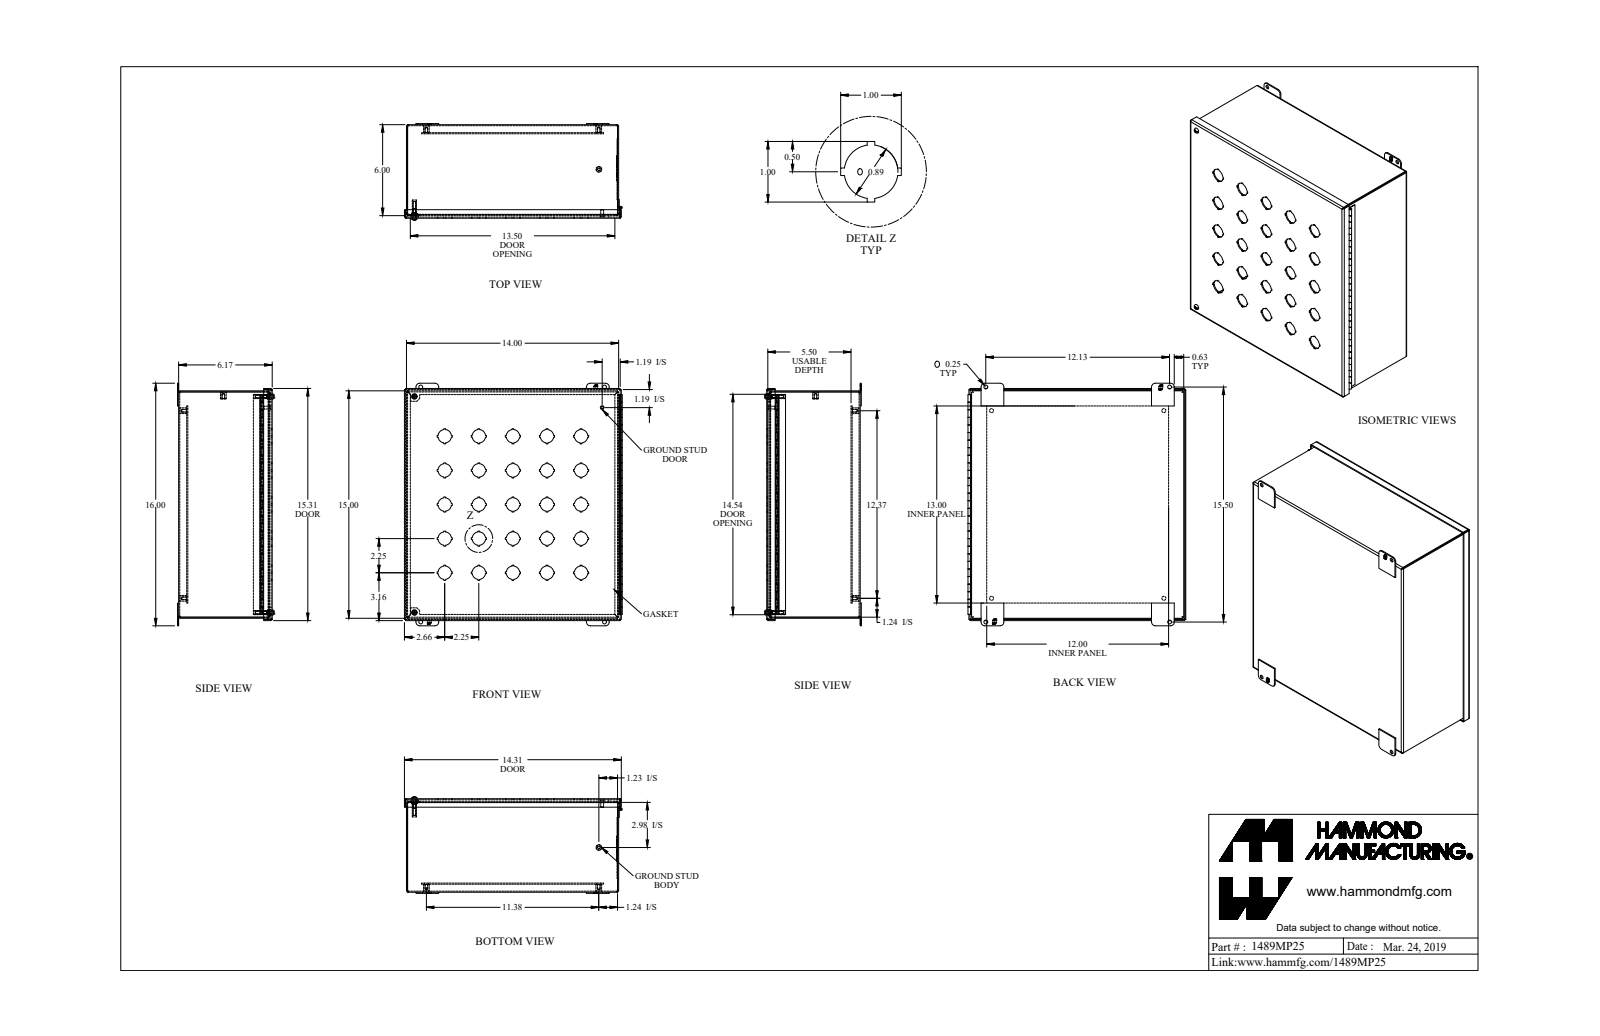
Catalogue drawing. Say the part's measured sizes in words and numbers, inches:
The part is named "1489MP25_Default". Its 3-D file was written by "SolidWorks 2019 (CONFIG_CONTROL_DESIGN)". It is 21 solids with 1167 faces: 814 planar, 295 cylindrical and 58 other. Overall it measures 16 by 14.373 by 6.371 inches. Its volume is 77.55 cubic inches and its surface area 2 084 square inches. Round holes: 25 of diameter 0.886, 6 of diameter 0.25, 5 of diameter 0.156, 4 of diameter 0.265, 2 of diameter 0.159, 2 of diameter 0.406. Round bosses or shafts: 5 of diameter 0.375, 2 of diameter 0.39, 2 of diameter 0.275, 2 of diameter 0.19, 2 of diameter 0.148, 1 of diameter 0.25, 1 of diameter 0.188, 1 of diameter 0.174. Partial cylindrical surfaces (rounded edges, fillets, slot ends): 12 of radius 0.036, 12 of radius 0.108, 8 of radius 0.25, 2 of radius 0.16, 2 of radius 0.171, 1 of radius 0.125. The main face-to-face distances are 0.072, 6.1, 5.568, 0.532, 6.172, 6.028, 13.928, 0.604, 14.928, 5.64. The hole center spacings are 5.031, 2.25, 3.182, 7.115, 4.5, 8.113, 6.75, 6.364.
